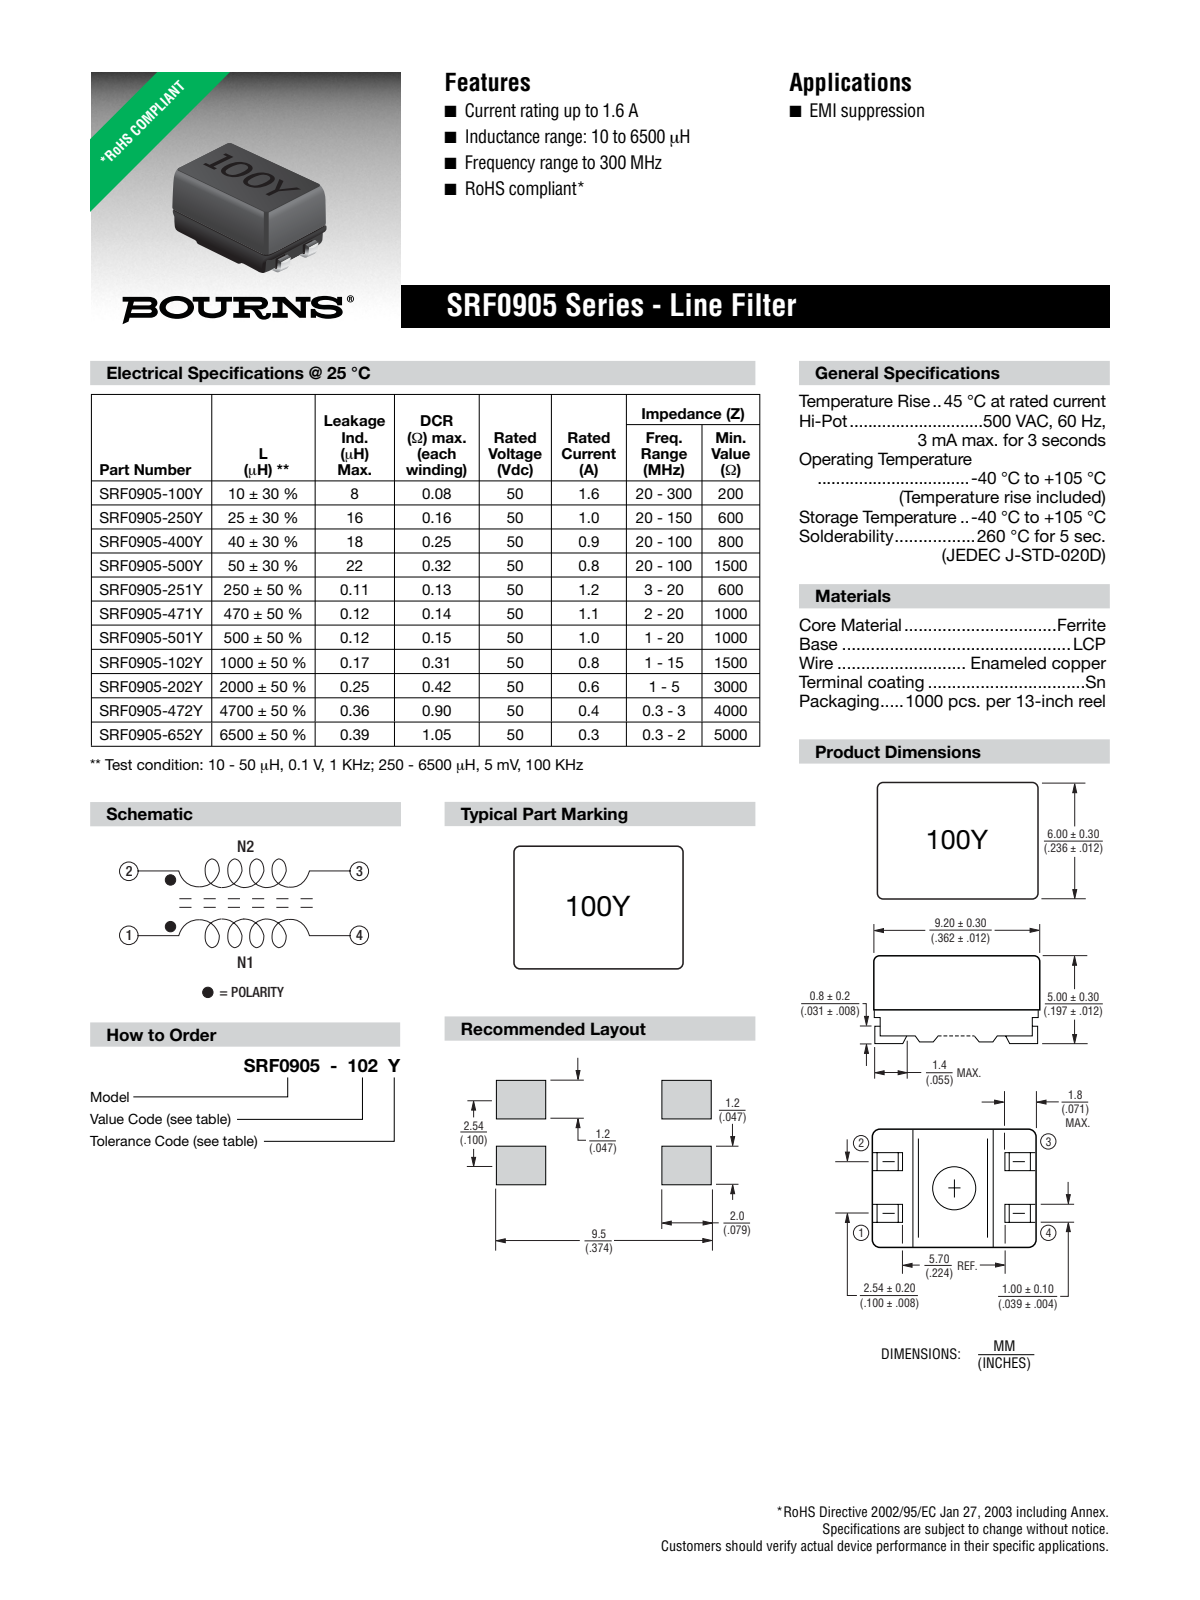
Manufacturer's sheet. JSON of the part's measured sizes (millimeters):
{"step_written_by": "ZW3D to STEP translator (CONFIG_CONTROL_DESIGN)", "units": "millimeters", "bodies": {"solids": 6, "faces": 157, "planar": 0, "cylindrical": 0, "other": 157}, "overall_size": [9.2, 6, 4.8], "volume_mm3": 152, "surface_area_mm2": 447}
